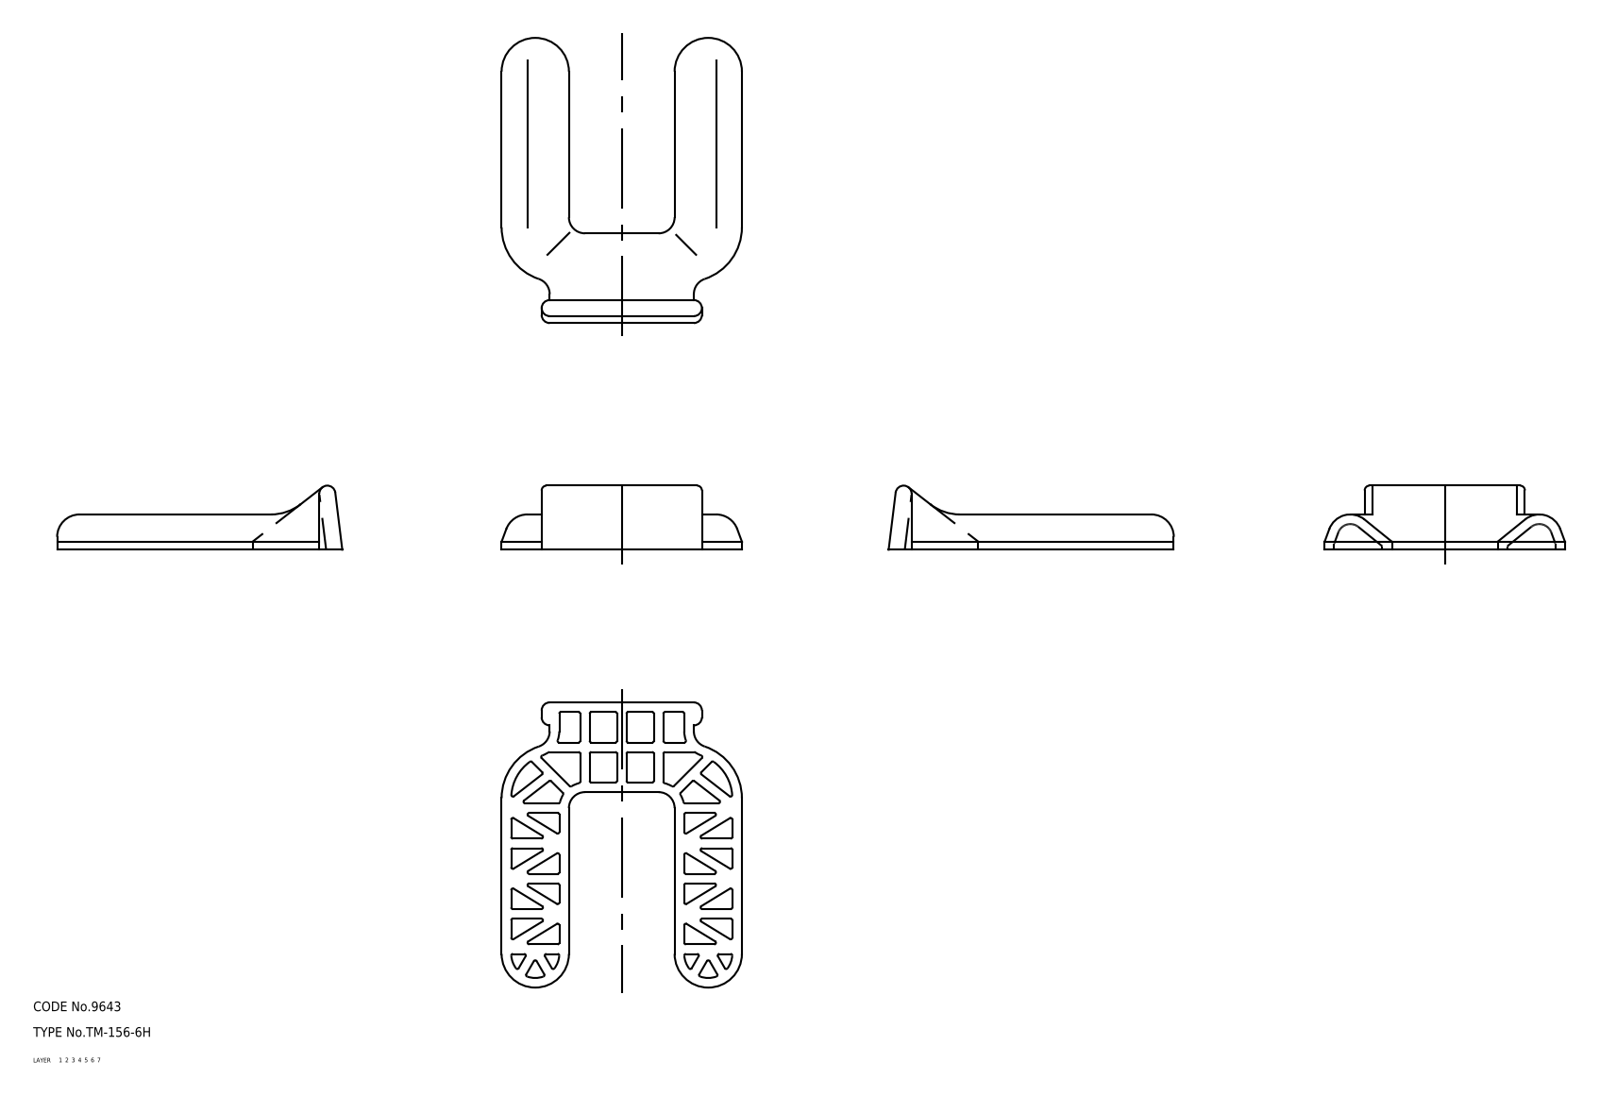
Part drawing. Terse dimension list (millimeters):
name: 67129692
written by: CADfix (AUTOMOTIVE_DESIGN)
unit: mm
bodies: 1 solid, 364 faces (0 planar, 0 cylindrical, 364 other)
size: 89 × 75 × 20
volume: 29 918 mm³; area: 17 842 mm²
